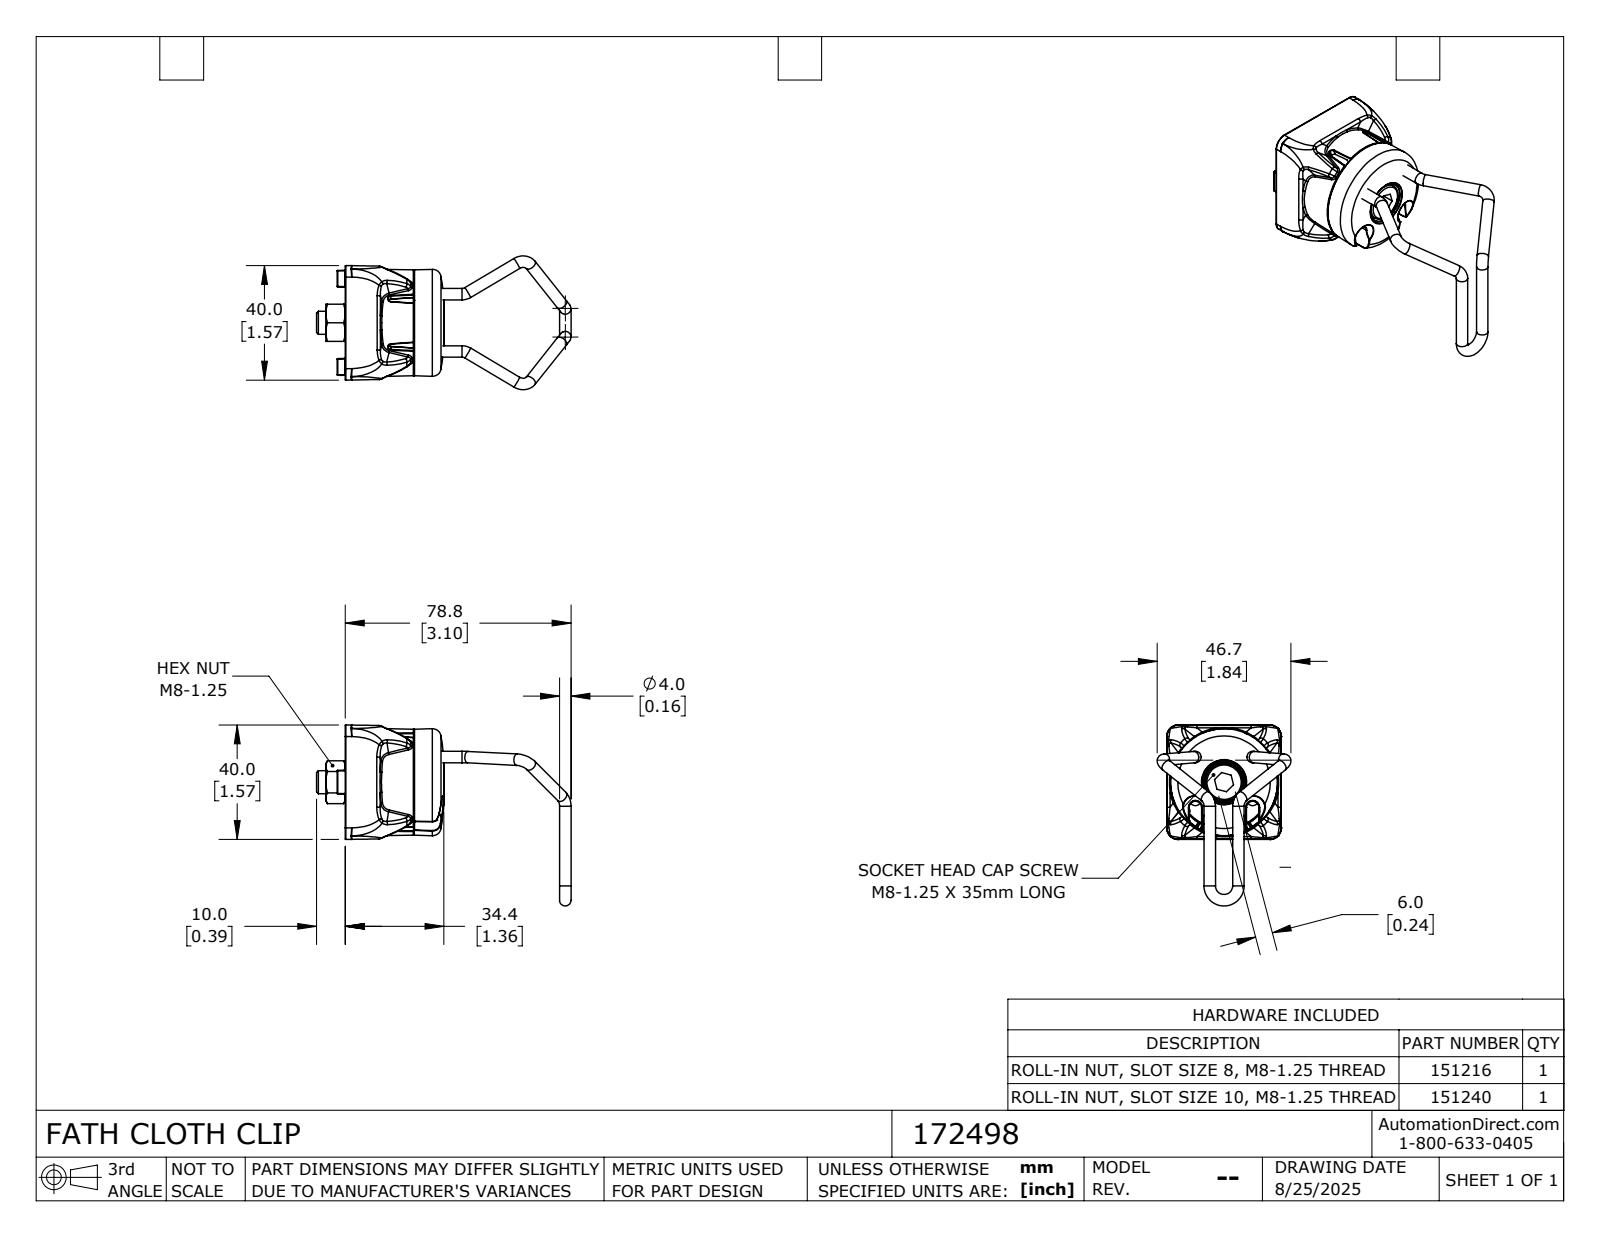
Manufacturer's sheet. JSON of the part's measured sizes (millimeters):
{"part_name": "172498", "step_written_by": "SolidWorks 2024 (CONFIG_CONTROL_DESIGN)", "units": "millimeters", "bodies": {"solids": 7, "faces": 1259, "planar": 222, "cylindrical": 308, "other": 729}, "overall_size": [88.85, 63.2, 46.72], "volume_mm3": 41250, "surface_area_mm2": 22498, "round_holes": [[6.8, 1], [8, 1], [13.01, 1]], "round_bosses_or_shafts": [[4, 12], [13, 1]], "partial_cylinders_radius": [[0.2, 142], [0.5, 22], [1, 8], [4, 8], [1.2, 4], [2.15, 2], [16.5, 1]], "face_to_face_distances": [13.5, 30.8, 8, 6, 13.3, 10.7, 17, 10.5, 24, 9.2]}
